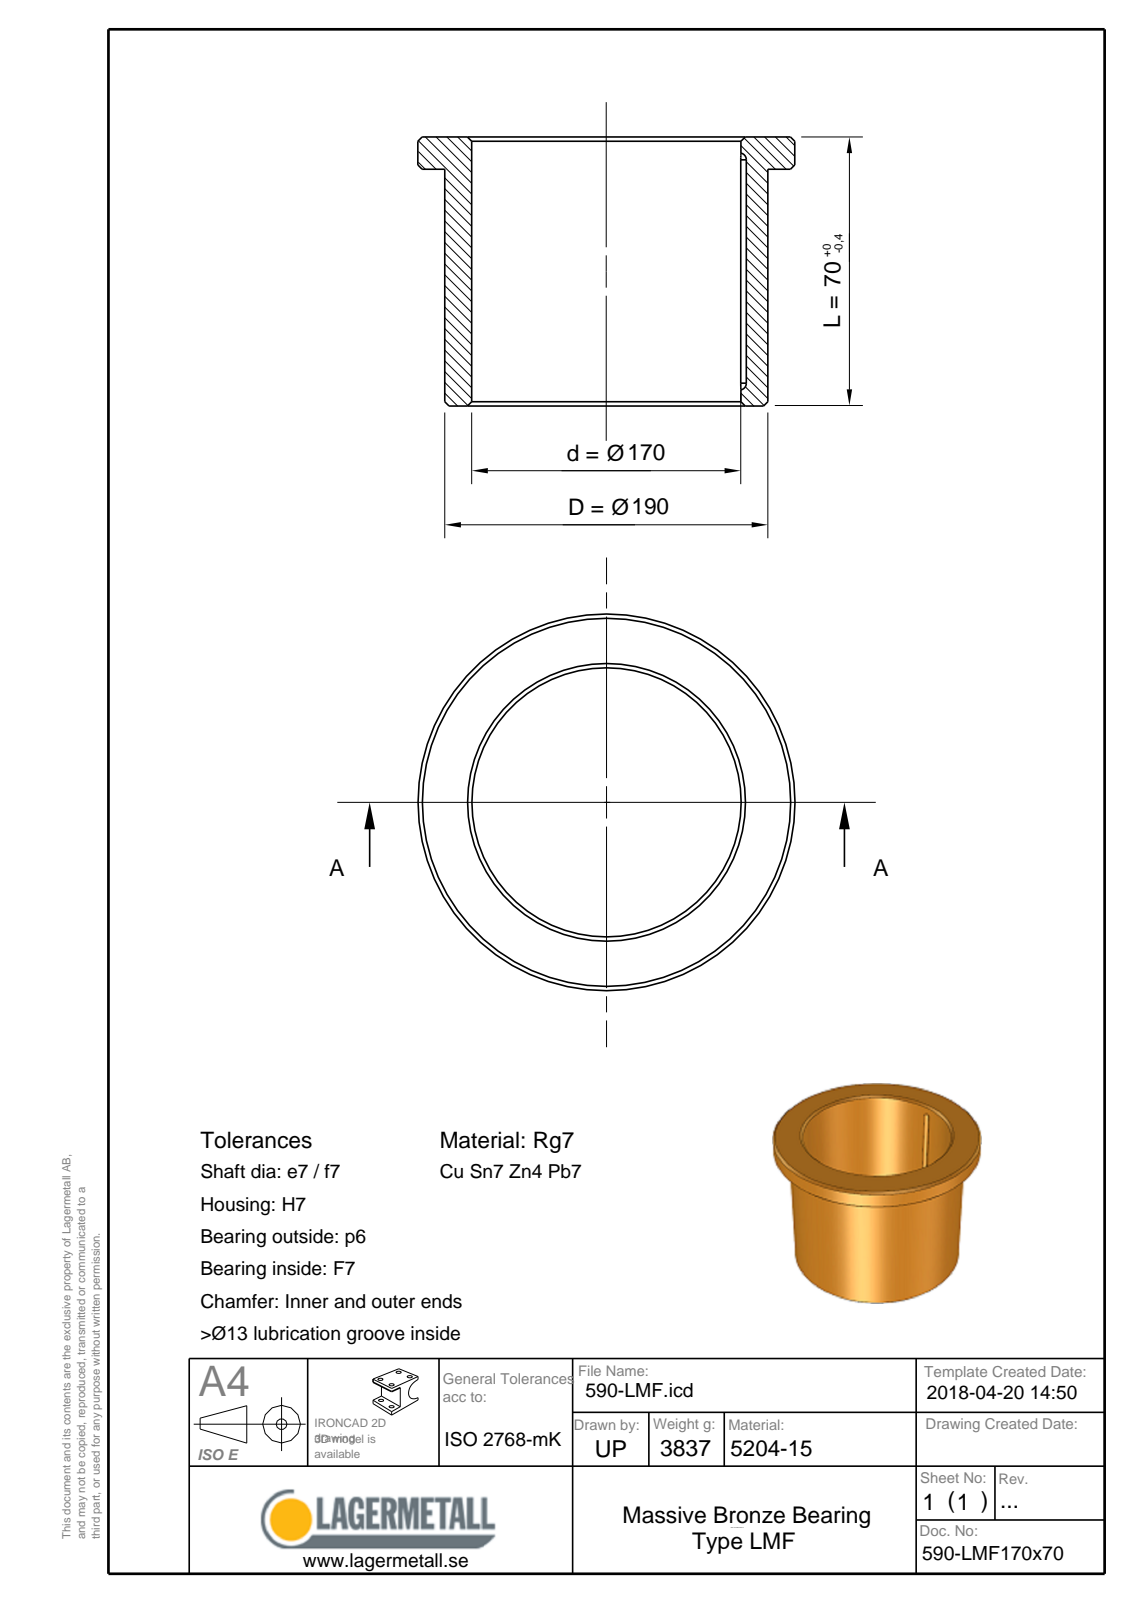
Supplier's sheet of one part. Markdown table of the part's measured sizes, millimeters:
| quantity | value |
| --- | --- |
| part name | 590-LMF170x70 |
| STEP written by | Spatial InterOp 3D (CONFIG_CONTROL_DESIGN) |
| units | millimeters |
| bodies | 1 solid, 16 faces (4 planar, 5 cylindrical, 7 other) |
| overall size | 205 × 205 × 70 |
| volume | 436 073 mm³ |
| surface area | 96 923 mm² |
| round holes (diameter × count) | 170 × 1 |
| round bosses / shafts (diameter × count) | 205 × 1, 190 × 1 |
| partial cylindrical surfaces (radius × count) | 2.25 × 2 |
| main face-to-face distances | 70, 60, 10 |
